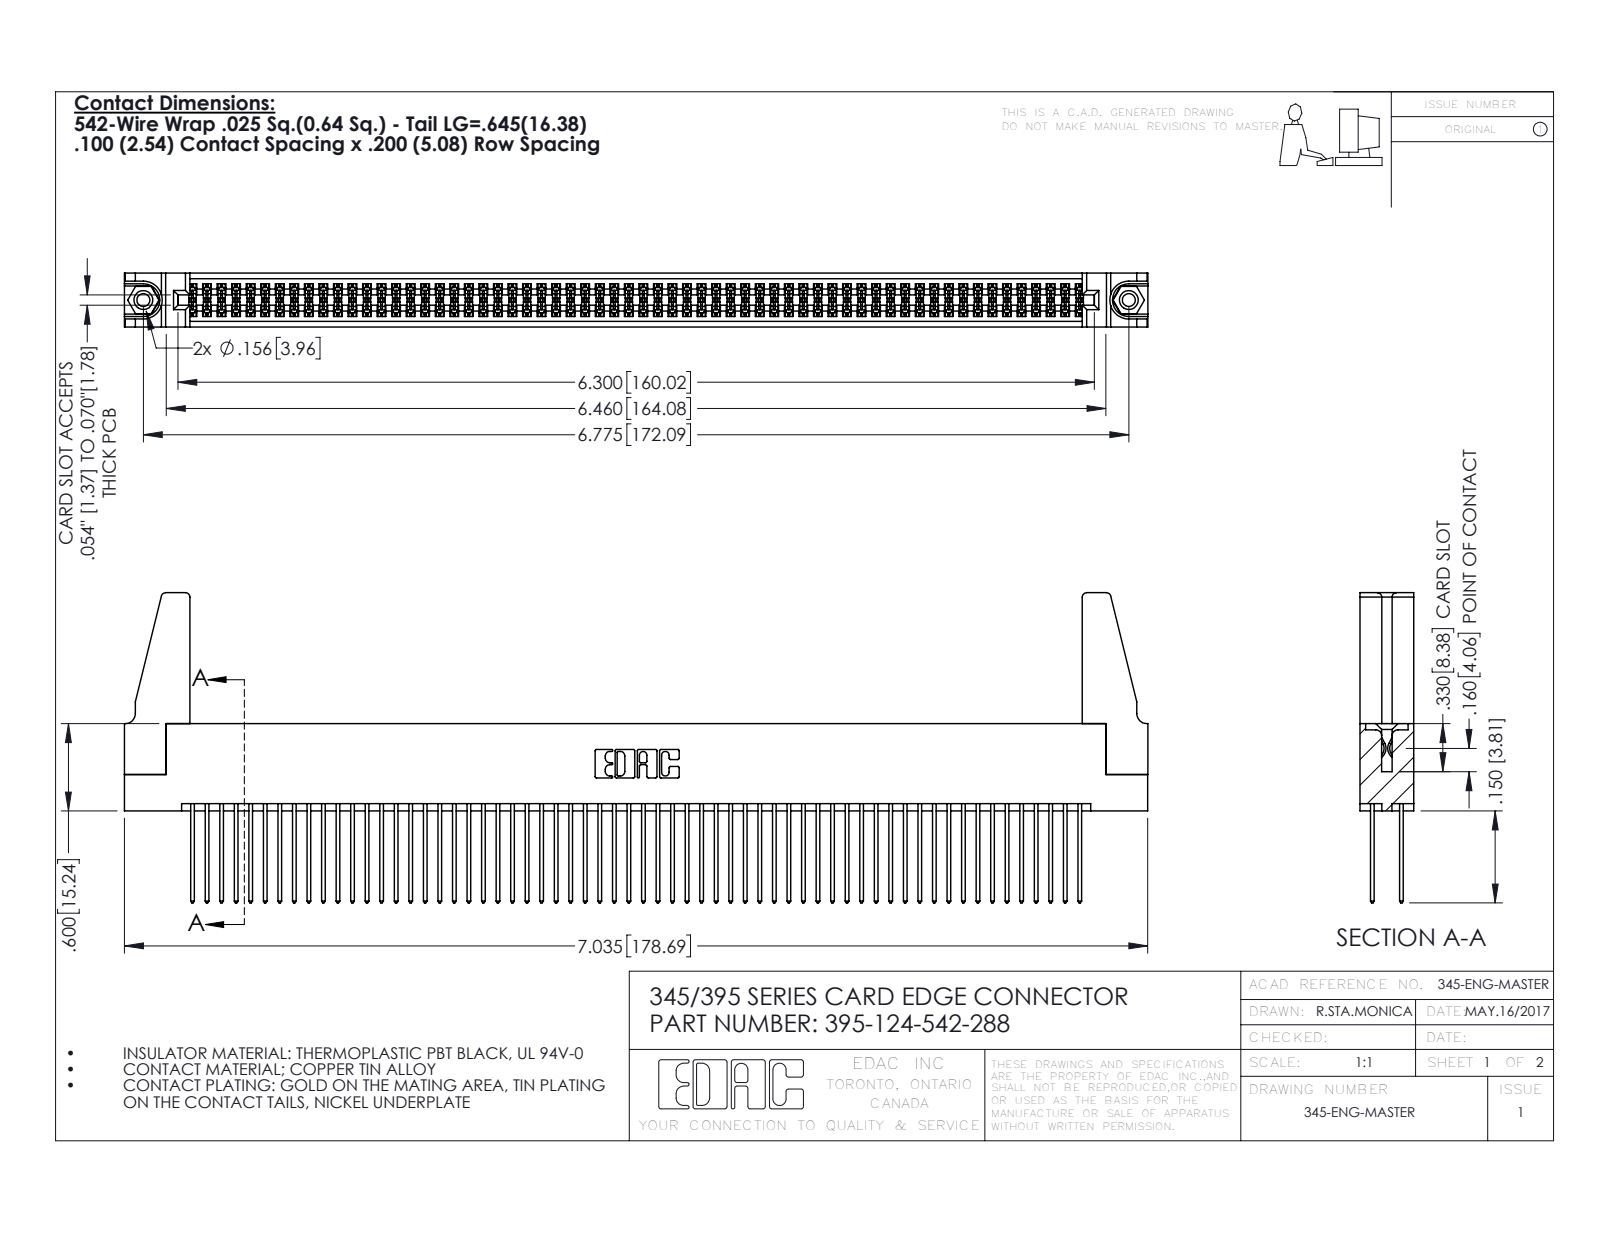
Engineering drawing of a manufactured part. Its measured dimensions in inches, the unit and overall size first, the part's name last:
Units: inches
Overall size (bounding box): 7.036 × 2.132 × 0.37
Round holes (diameter × count): ⌀0.089 ×2, ⌀0.125 ×2, ⌀0.156 ×2, ⌀0.064 ×1
Round bosses / shafts (diameter × count): ⌀0.155 ×2
Partial cylindrical surfaces — rounded edges, fillets, slot ends (radius × count): R0.006 ×186, R0.01 ×124, R0.01 ×22, R0.03 ×8, R0.007 ×6, R0.031 ×6, R0.026 ×3, R0.014 ×2
Main face-to-face distances: 0.072, 0.298, 0.2, 0.098, 0.272, 0.025, 0.37, 0.225, 0.175, 0.149
Hole centre spacings: 0.27, 6.539, 6.775
Volume: 1.304 in³ · Surface area: 51.15 in²
Bodies: 129 solids, 6450 faces (4244 planar, 2190 cylindrical, 16 other)
Part name (STEP PRODUCT): 345-250-001_345-250-001-102; 345-292-001_345-293-142; 395-124-542-288; 345 Part_Flush Mounting Lugs - 0.156 Dia-TH (+1 more)
STEP written by: SolidWorks 2016 (CONFIG_CONTROL_DESIGN)
